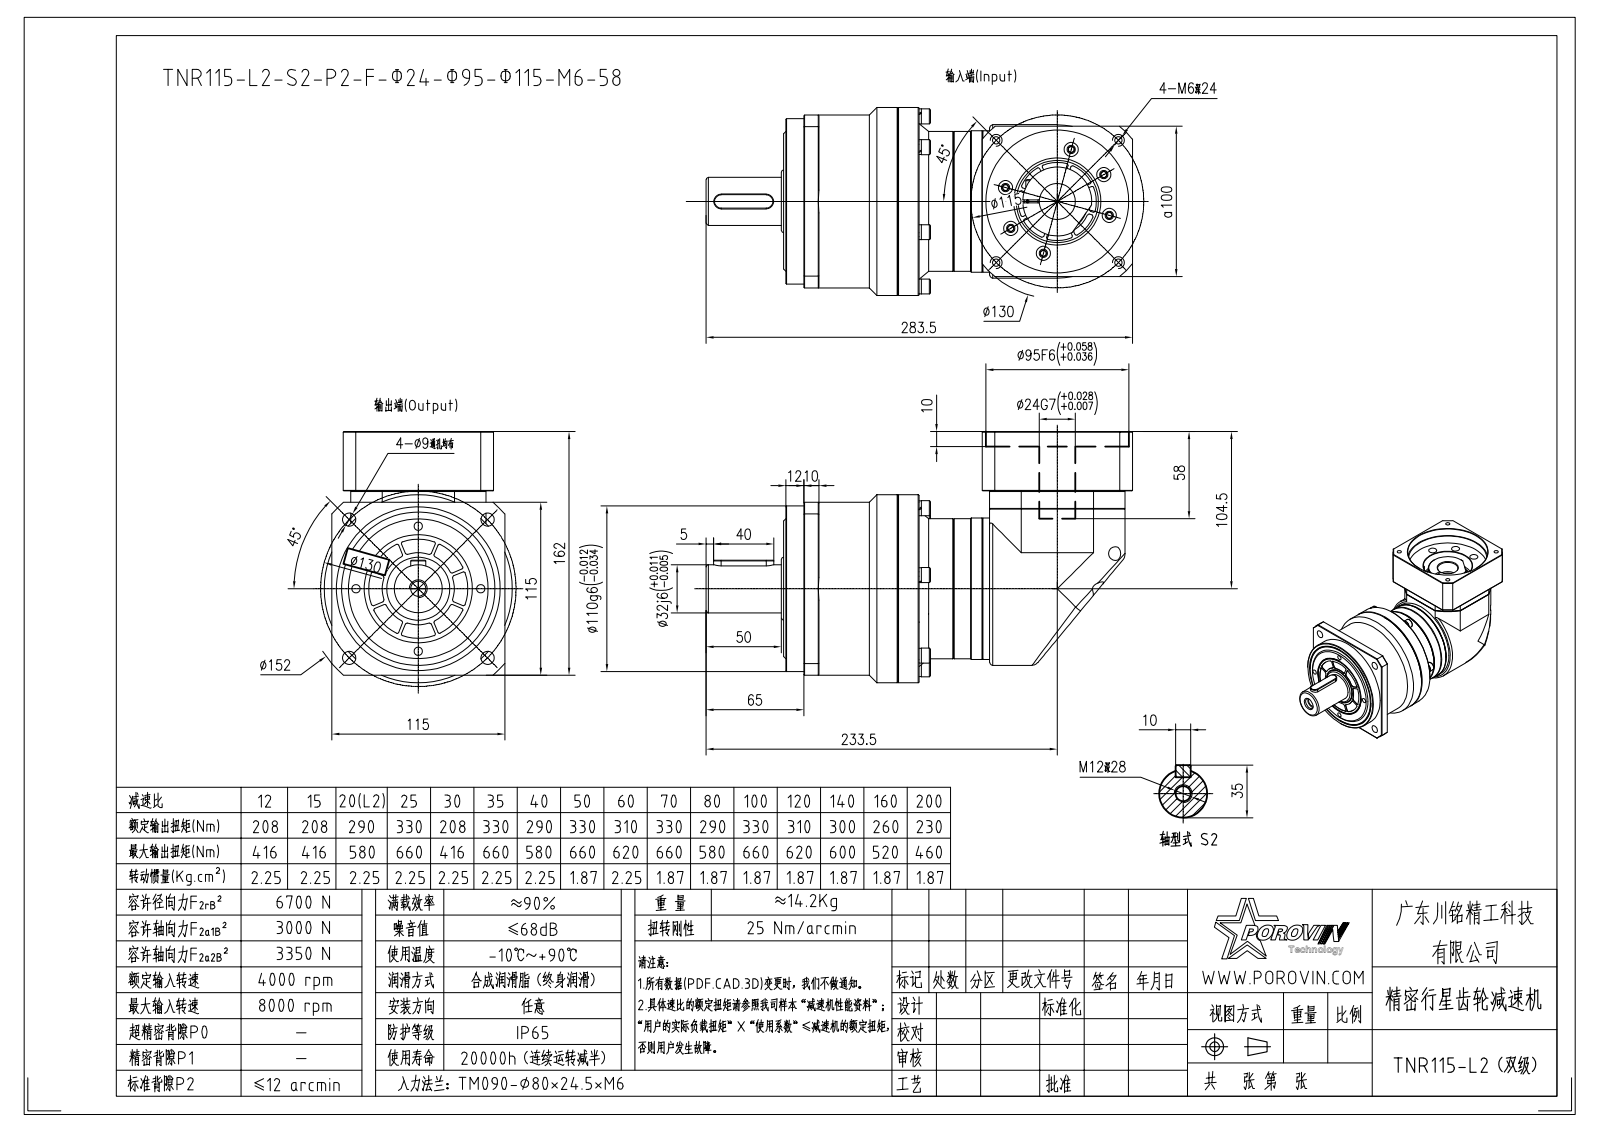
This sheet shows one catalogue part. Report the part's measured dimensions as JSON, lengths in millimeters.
{"part_name": "SPRING_LOCK_WASHERS--NORMA-3267; HEXAGON_SOCKET_HEAD_CAP_S-24980; HEXAGON_SOCKET_HEAD_CAP_S-24863; HEXAGON_SOCKET_HEAD_CAP_SC-3204 (+8 more)", "step_written_by": "CREO PARAMETRIC BY PTC INC, 2020053 (CONFIG_CONTROL_DESIGN)", "units": "millimeters", "bodies": {"solids": 62, "faces": 1635, "planar": 678, "cylindrical": 653, "other": 304}, "overall_size": [283.5, 167, 125], "volume_mm3": 2248000, "surface_area_mm2": 297278, "round_holes": [[5.5, 23], [5.4, 19], [9.5, 12], [5, 9], [9.2, 7], [4.2, 6], [6.6, 6], [6.68, 6], [9, 4], [10.2, 2], [6.5, 1], [13, 1]], "round_bosses_or_shafts": [[8.5, 19], [8, 19], [5, 19], [10, 7], [6, 7], [9.88, 6], [125, 1], [115, 1]], "partial_cylinders_radius": [[1, 76], [5, 3], [4, 1], [5.25, 1], [51, 1], [65, 1], [76, 1]], "face_to_face_distances": [37, 19.5, 5, 12, 56.5, 56.3, 19.3, 95, 90, 100], "hole_center_spacings": [35.75, 57.25, 40.75, 46.18, 98.8, 24.76, 46.25, 58.16]}
